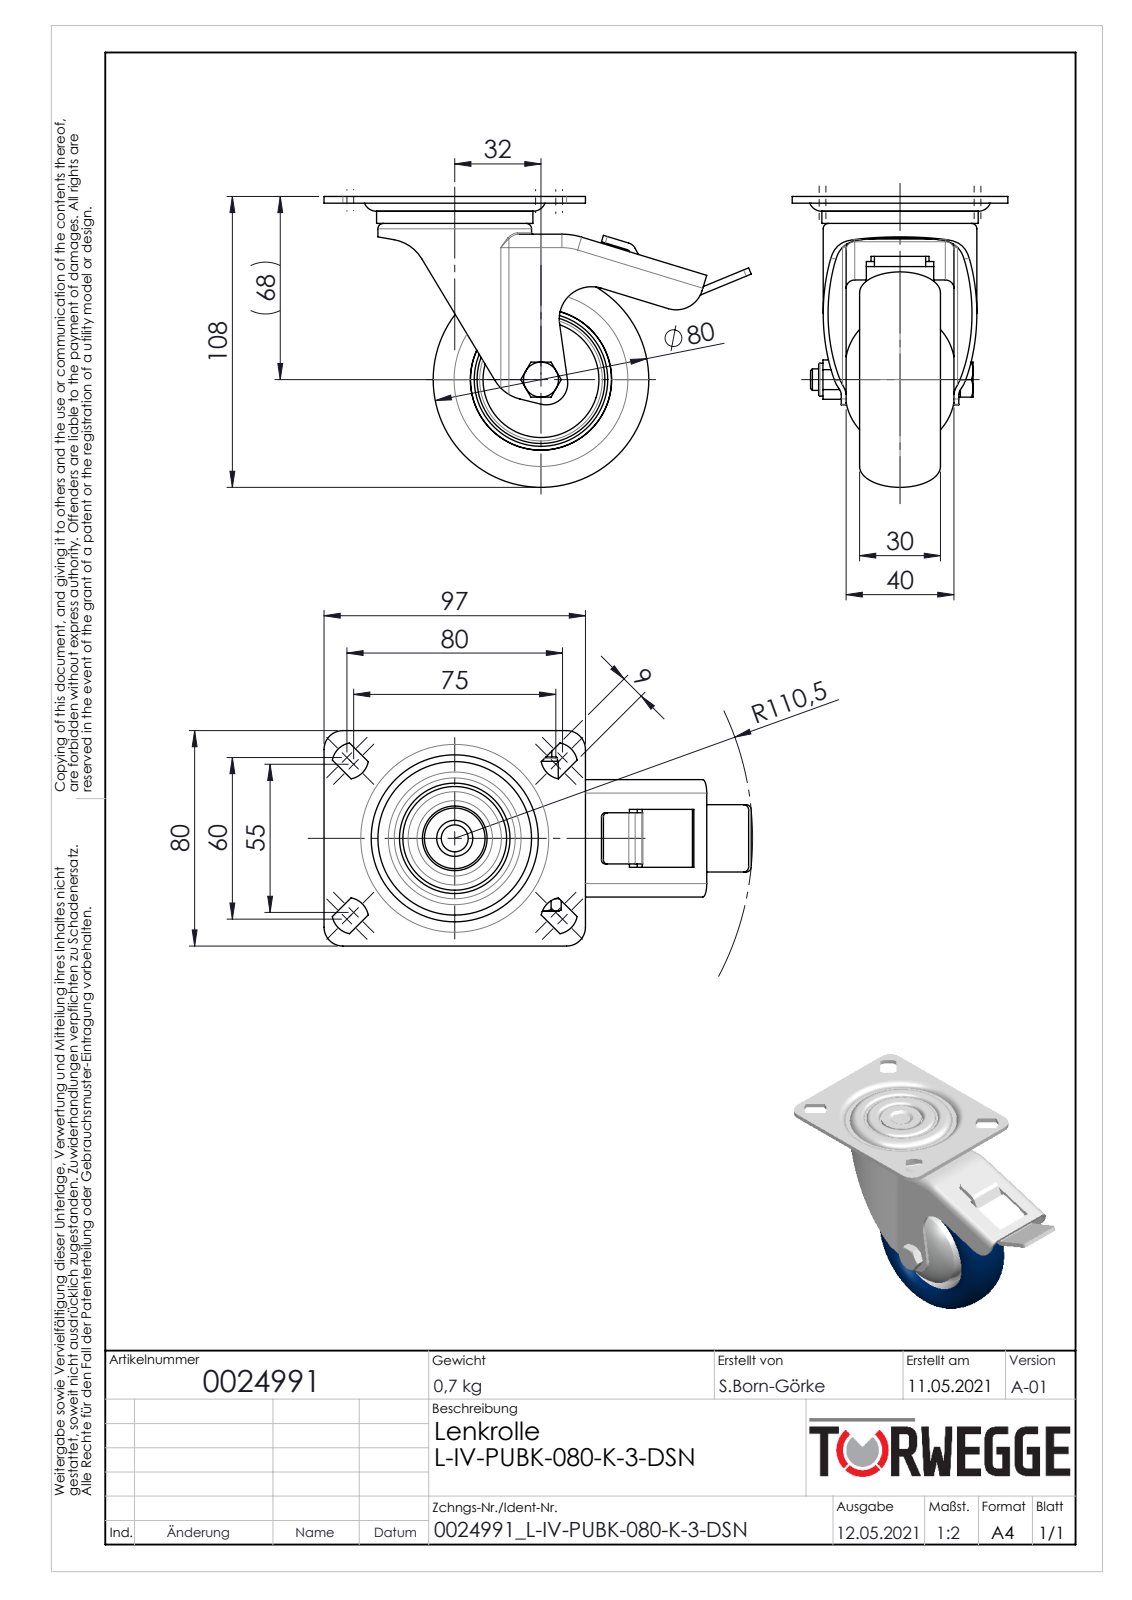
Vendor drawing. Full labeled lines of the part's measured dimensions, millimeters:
Part name (STEP PRODUCT): 0024991
STEP written by: SolidWorks 2020 (AUTOMOTIVE_DESIGN)
Units: millimetres
Bodies: 8 solids, 303 faces (104 planar, 87 cylindrical, 112 other)
Overall size (bounding box): 158.5 × 108 × 80
Volume: 176 858 mm³ · Surface area: 94 817 mm²
Round holes (diameter × count): ⌀6.65 ×1, ⌀8 ×1, ⌀8.3 ×1, ⌀10 ×1, ⌀24 ×1, ⌀33 ×1, ⌀35 ×1, ⌀53.4 ×1
Round bosses / shafts (diameter × count): ⌀58 ×1, ⌀57 ×1, ⌀29 ×1, ⌀22.5 ×1, ⌀15 ×1, ⌀13 ×1, ⌀12.2 ×1
Partial cylindrical surfaces — rounded edges, fillets, slot ends (radius × count): R8.07 ×8, R5 ×6, R3.2 ×4, R7 ×4, R4 ×3, R1 ×2, R1.5 ×2, R2 ×2
Main face-to-face distances: 2.5, 1.8, 3, 5.5, 41.8, 9.3, 40, 6.3, 11.8, 8.5
